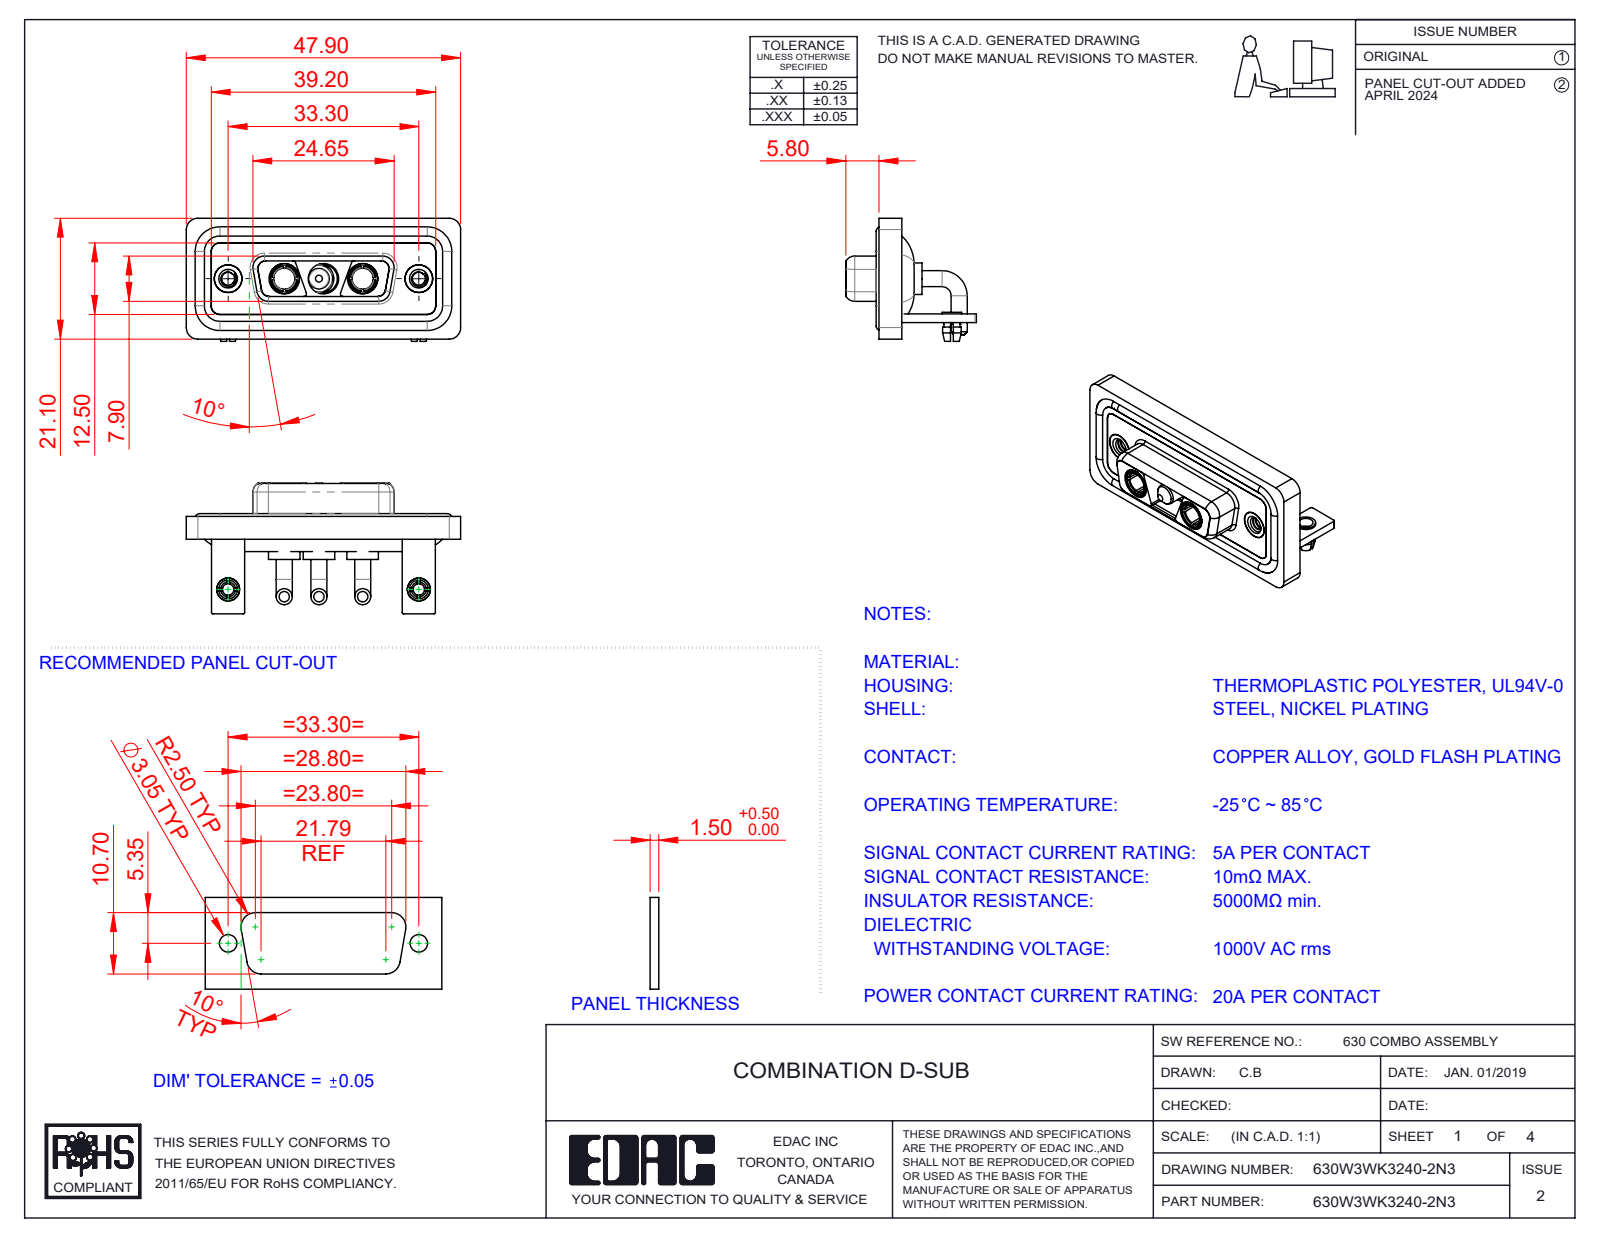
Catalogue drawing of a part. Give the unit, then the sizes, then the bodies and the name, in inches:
Units: inches
Overall size (bounding box): 1.886 × 0.898 × 0.846
Round holes (diameter × count): ⌀0.191 ×5, ⌀0.209 ×3, ⌀0.079 ×2, ⌀0.089 ×2, ⌀0.098 ×2, ⌀0.126 ×2, ⌀0.146 ×2, ⌀0.157 ×2, ⌀0.159 ×2, ⌀0.197 ×2
Round bosses / shafts (diameter × count): ⌀0.11 ×6, ⌀0.063 ×4, ⌀0.217 ×3, ⌀0.205 ×3, ⌀0.187 ×3, ⌀0.148 ×3, ⌀0.195 ×2, ⌀0.195 ×2
Partial cylindrical surfaces — rounded edges, fillets, slot ends (radius × count): R0.079 ×21, R0.059 ×18, R0.01 ×16, R0.053 ×12, R0.02 ×9, R0.063 ×8, R0.024 ×4, R0.026 ×4
Main face-to-face distances: 0.016, 0.114, 0.059, 0.146, 0.071, 0.043, 0.161, 0.063, 0.098, 0.055
Hole centre spacings: 0.27, 0.386, 0.656, 0.925, 1.311, 0.539
Volume: 0.393 in³ · Surface area: 16.56 in²
Bodies: 17 solids, 735 faces (246 planar, 320 cylindrical, 169 other)
Part name (STEP PRODUCT): 630Combo Threaded Rivet_2; 630Combo Housing_3WK3; 630Combo Shell Front_15 Contacts; Power Socket_20A RA (+6 more)
STEP written by: SolidWorks 2023 (CONFIG_CONTROL_DESIGN)
